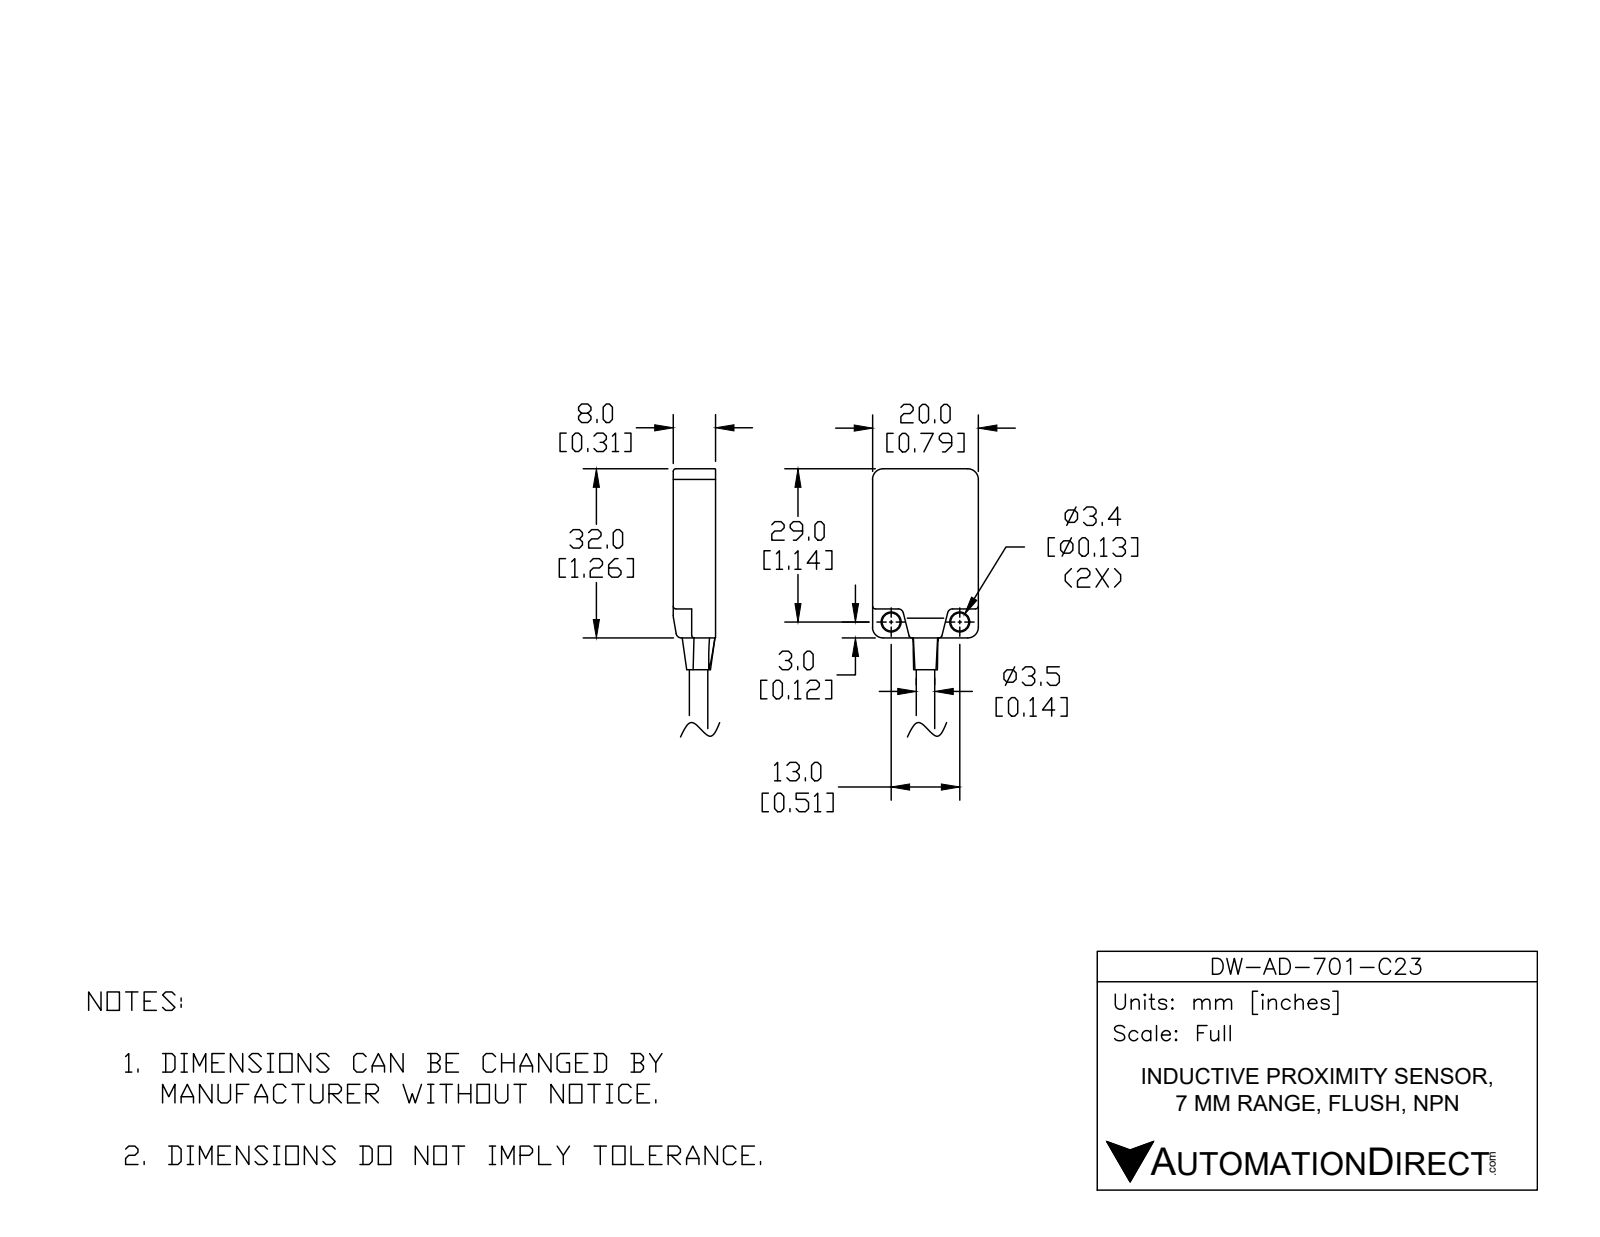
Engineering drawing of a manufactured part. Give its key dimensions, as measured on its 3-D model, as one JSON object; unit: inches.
{"part_name": "DW-AD-701-C23", "step_written_by": "SolidWorks 2017 (AUTOMOTIVE_DESIGN)", "units": "inches", "bodies": {"solids": 1, "faces": 97, "planar": 37, "cylindrical": 36, "other": 24}, "overall_size": [5.237, 0.787, 0.315], "volume_in3": 0.344, "surface_area_in2": 4.965, "round_holes": [[0.134, 2]], "round_bosses_or_shafts": [[0.039, 3], [0.13, 1]], "partial_cylinders_radius": [[0.02, 10], [0.039, 6], [0.02, 4], [0.022, 4], [0.079, 4]], "face_to_face_distances": [0.315, 0.787, 1.26, 0.177, 0.138, 1.043, 0.217, 0.037, 0.039, 0.713], "hole_center_spacings": [0.512]}
